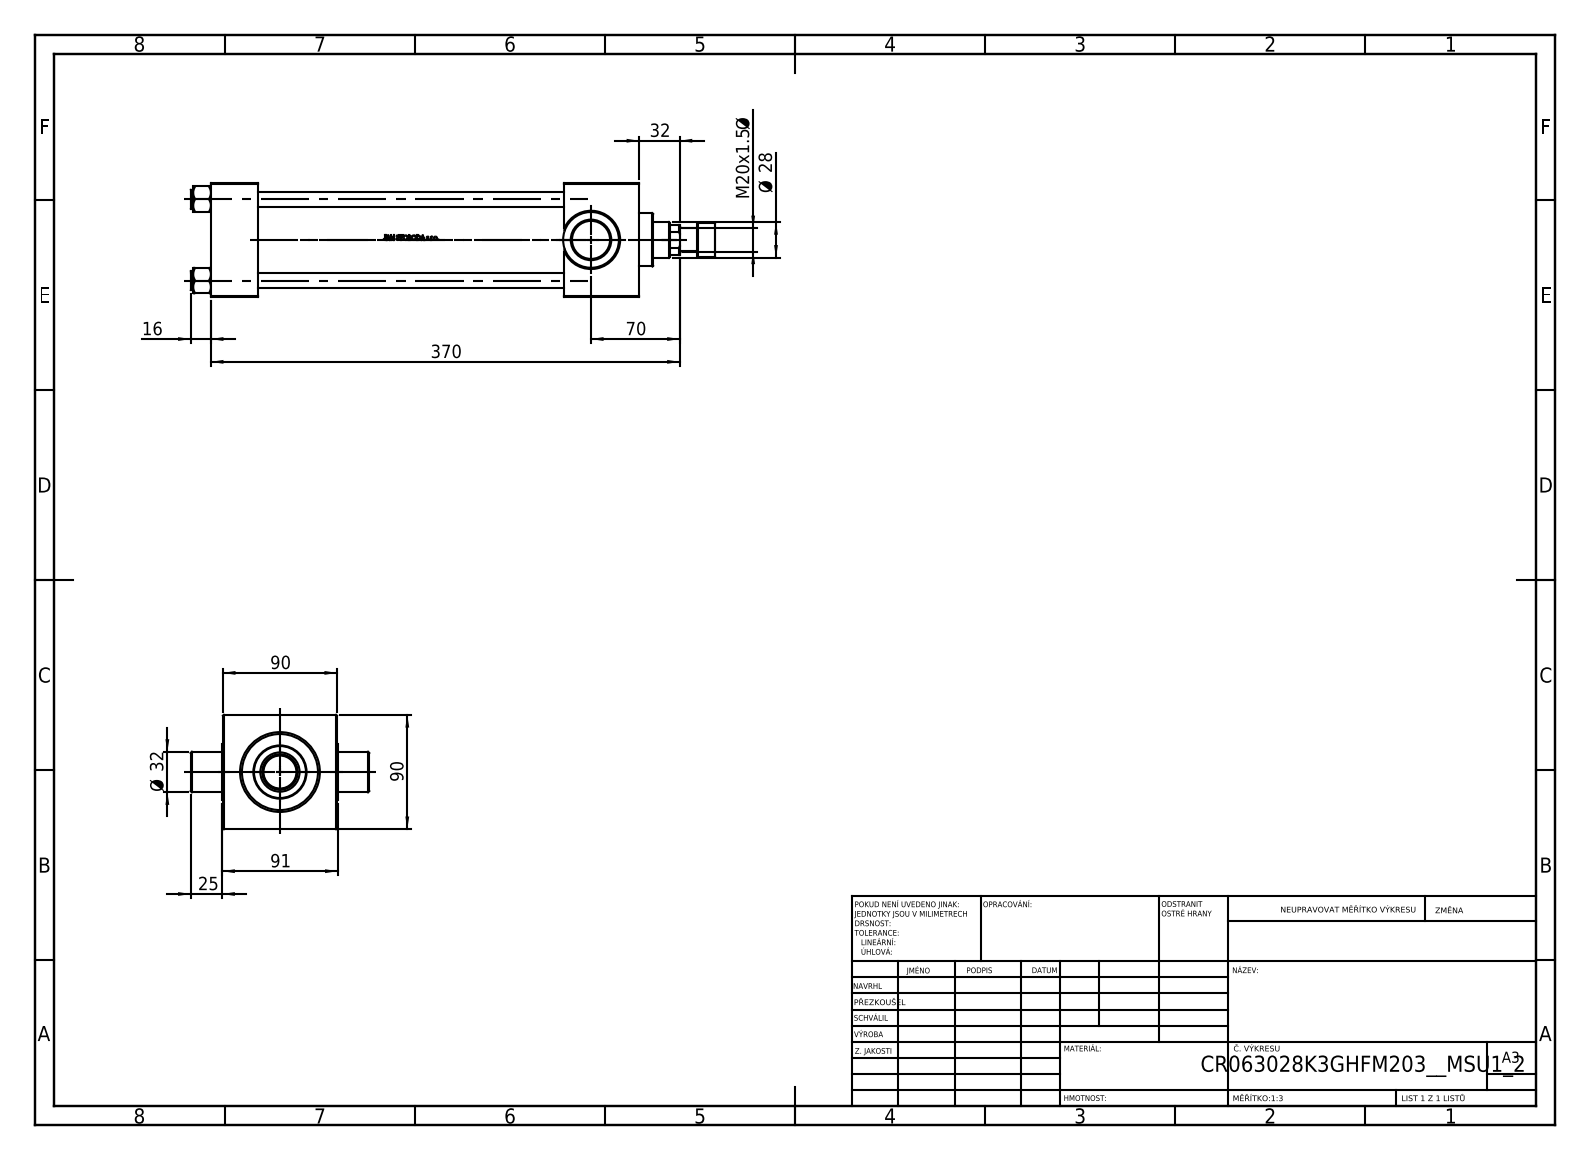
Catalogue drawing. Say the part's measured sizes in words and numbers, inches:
The part is named "V215_VC_A; V215CR_VCP_K; V215CR_K_Body; NUT_M5_K (+2 more)". Its 3-D file was written by "SolidWorks 2019 (CONFIG_CONTROL_DESIGN)". It is 12 solids with 1079 faces: 433 planar, 116 cylindrical and 530 other. Overall it measures 16.299 by 5.551 by 3.543 inches. Its volume is 80.86 cubic inches and its surface area 464.5 square inches. Round holes: 4 of diameter 0.472, 1 of diameter 0.276, 1 of diameter 0.728, 1 of diameter 1.102, 1 of diameter 1.22, 1 of diameter 1.969, 1 of diameter 2.362, 1 of diameter 2.48. Round bosses or shafts: 4 of diameter 0.591, 1 of diameter 2.717, 1 of diameter 1.654, 1 of diameter 1.26, 1 of diameter 1.063, 1 of diameter 0.709. Partial cylindrical surfaces (rounded edges, fillets, slot ends): 1 of radius 0.866. The main face-to-face distances are 3.543, 1.457, 0.02, 3.524, 13.307, 11.85, 9.528, 10.984, 2.323, 3.504. The hole center spacings are 1.79, 2.531, 3.58.
